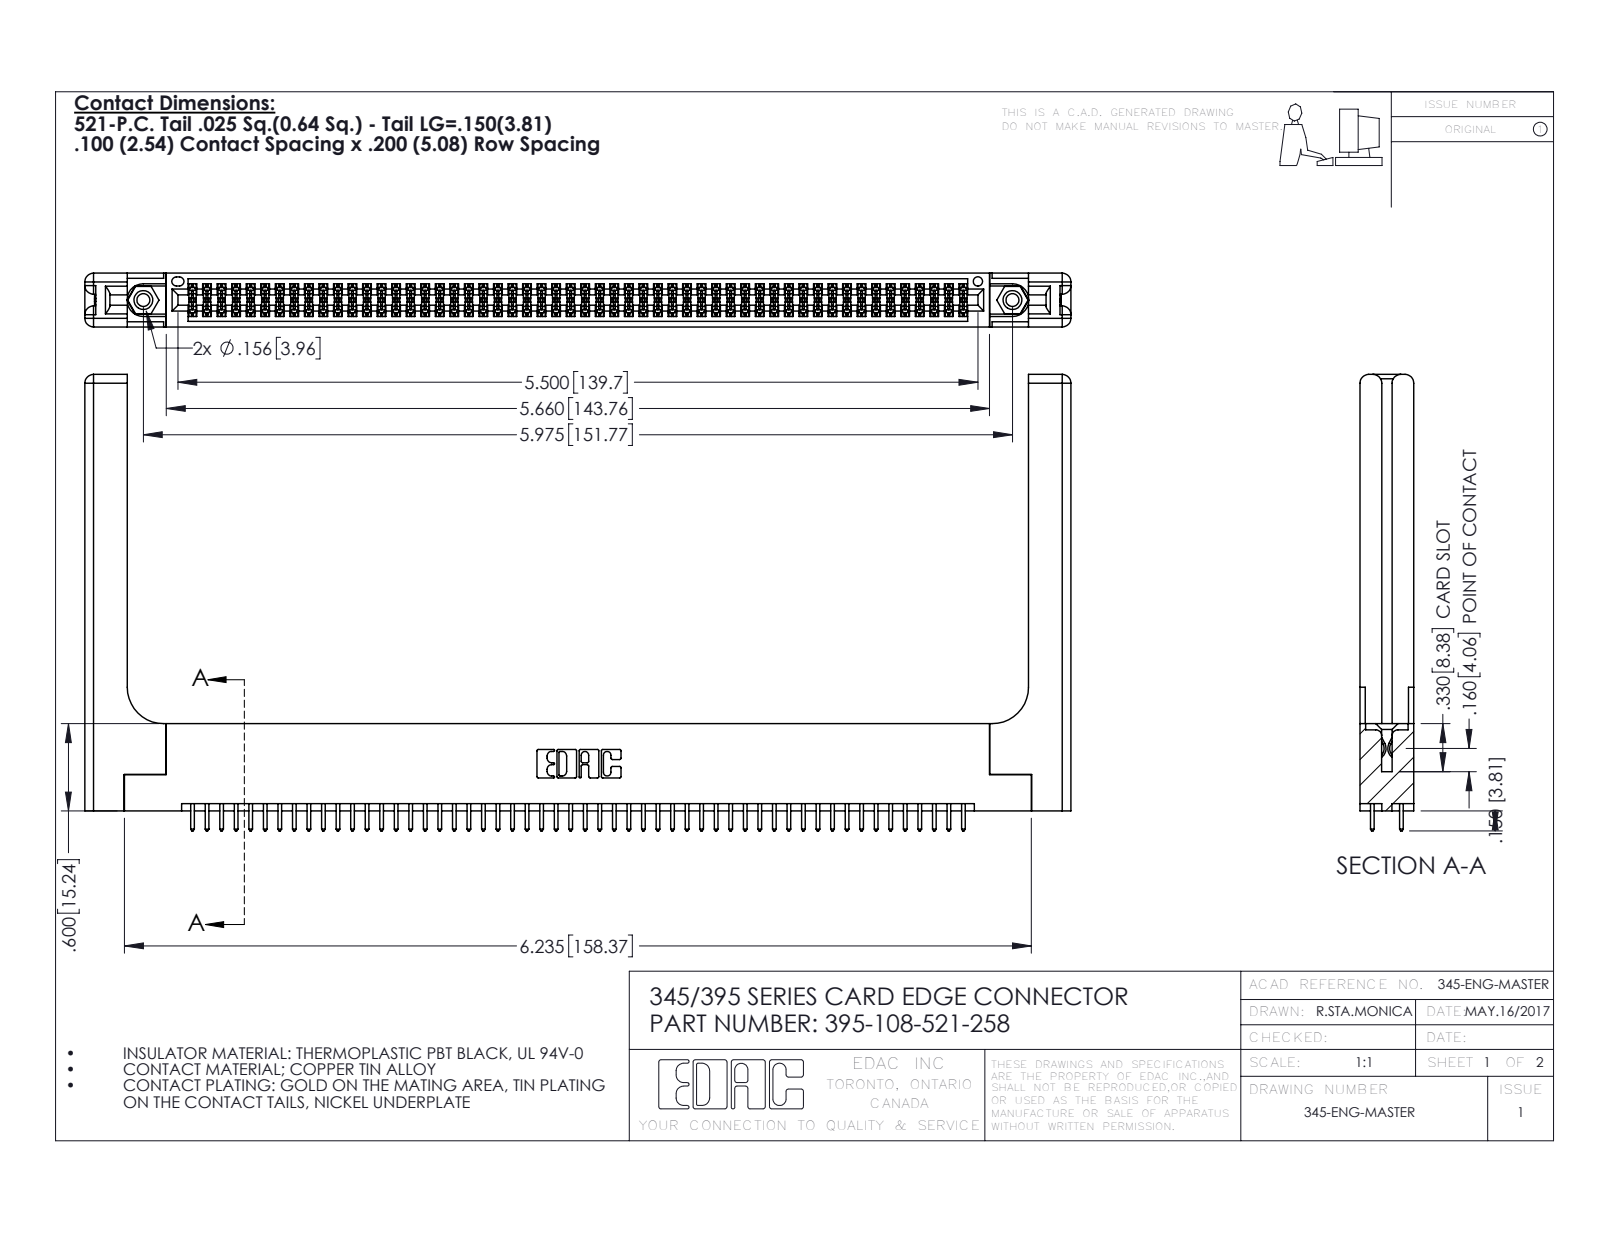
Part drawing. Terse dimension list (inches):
name: 345-292-001_345-293-121; 345-250-001_345-250-001-102; 345-220-058_345-220-058; 395-108-521-258 (+1 more)
written by: SolidWorks 2016 (CONFIG_CONTROL_DESIGN)
unit: in
bodies: 113 solids, 5782 faces (3792 planar, 1930 cylindrical, 60 other)
size: 6.779 × 3.137 × 0.37
volume: 1.542 in³; area: 46.23 in²
holes: 2× ⌀0.089, 2× ⌀0.125, 2× ⌀0.156, 1× ⌀0.064
bosses: 2× ⌀0.155
rounds: 162× R0.006, 108× R0.01, 22× R0.01, 16× R0.06, 6× R0.007, 6× R0.031, 3× R0.026, 2× R0.014
face distances: 0.072, 0.298, 0.37, 0.2, 0.098, 0.272, 0.025, 0.225, 0.148, 0.15
hole spacings: 0.27, 5.739, 5.975
